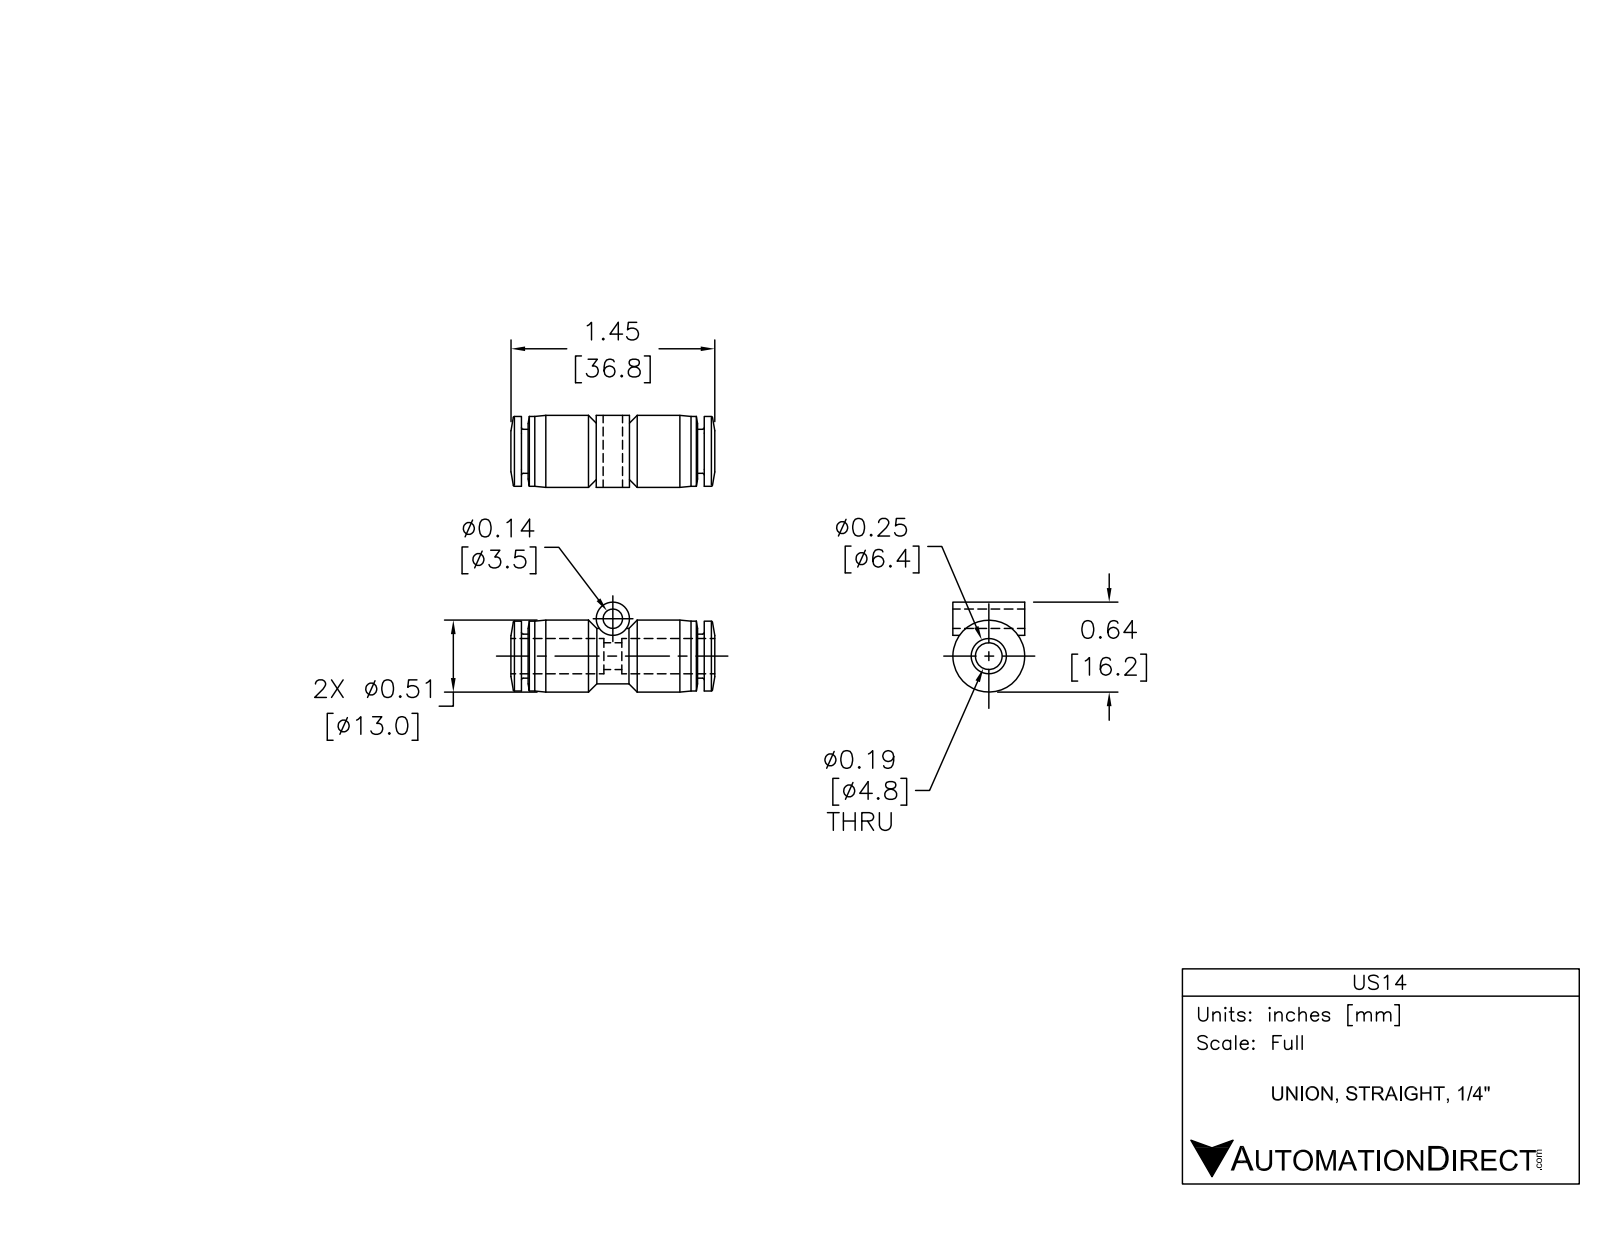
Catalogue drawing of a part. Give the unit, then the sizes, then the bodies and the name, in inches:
Units: inches
Overall size (bounding box): 1.449 × 0.64 × 0.512
Round holes (diameter × count): ⌀0.138 ×1, ⌀0.189 ×1, ⌀0.258 ×1
Round bosses / shafts (diameter × count): ⌀0.512 ×1, ⌀0.496 ×1, ⌀0.394 ×1, ⌀0.313 ×1, ⌀0.236 ×1
Main face-to-face distances: 1.299, 0.047, 1.252, 0.587, 0.713, 0.539, 0.665, 1.205, 0.512, 0.126
Volume: 0.195 in³ · Surface area: 4.621 in²
Bodies: 1 solid, 68 faces (8 planar, 28 cylindrical, 32 other)
Part name (STEP PRODUCT): US14
STEP written by: SolidWorks 2015 (AUTOMOTIVE_DESIGN)
